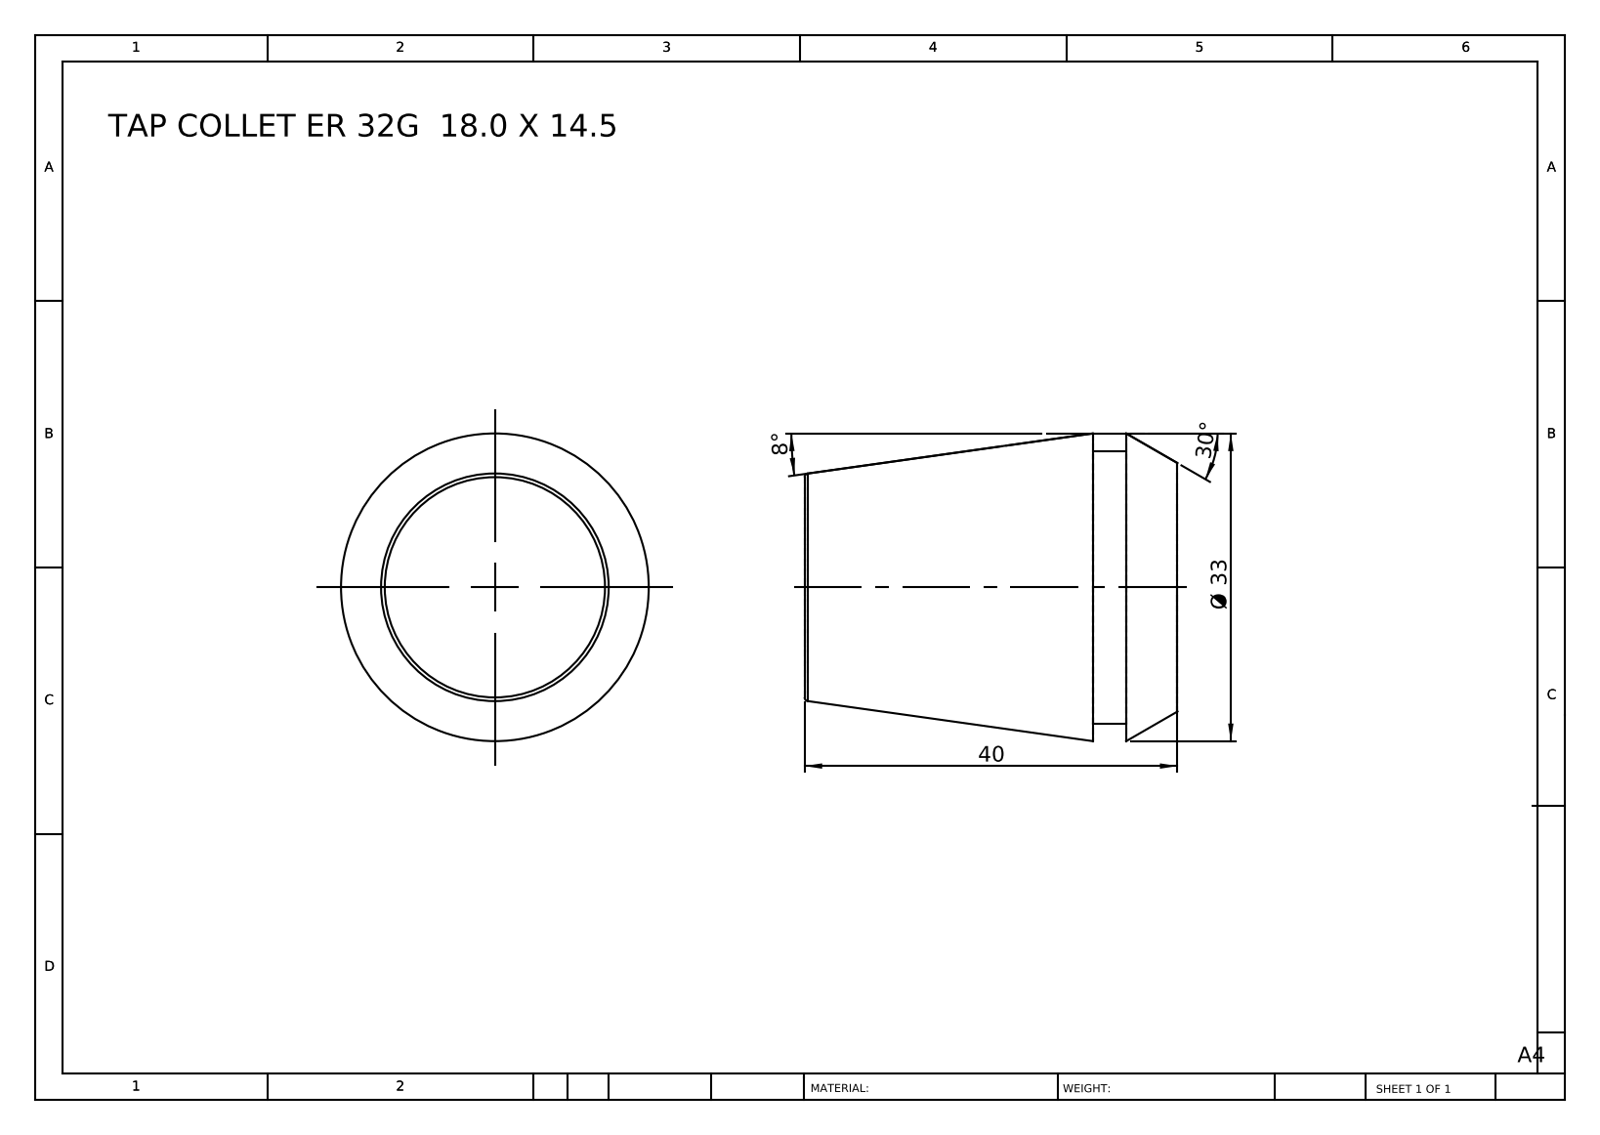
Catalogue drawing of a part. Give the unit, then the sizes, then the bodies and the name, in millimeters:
Units: millimetres
Overall size (bounding box): 40 × 33 × 33
Round bosses / shafts (diameter × count): ⌀29.2 ×1
Main face-to-face distances: 40, 9.1, 30.9, 5.5, 3.6, 34.5
Volume: 26 350 mm³ · Surface area: 5 119 mm²
Bodies: 1 solid, 12 faces (4 planar, 2 cylindrical, 6 other)
Part name (STEP PRODUCT): TAP COLLET ER 32G 18.0 X 14.5
STEP written by: SolidWorks 2014 (CONFIG_CONTROL_DESIGN)
